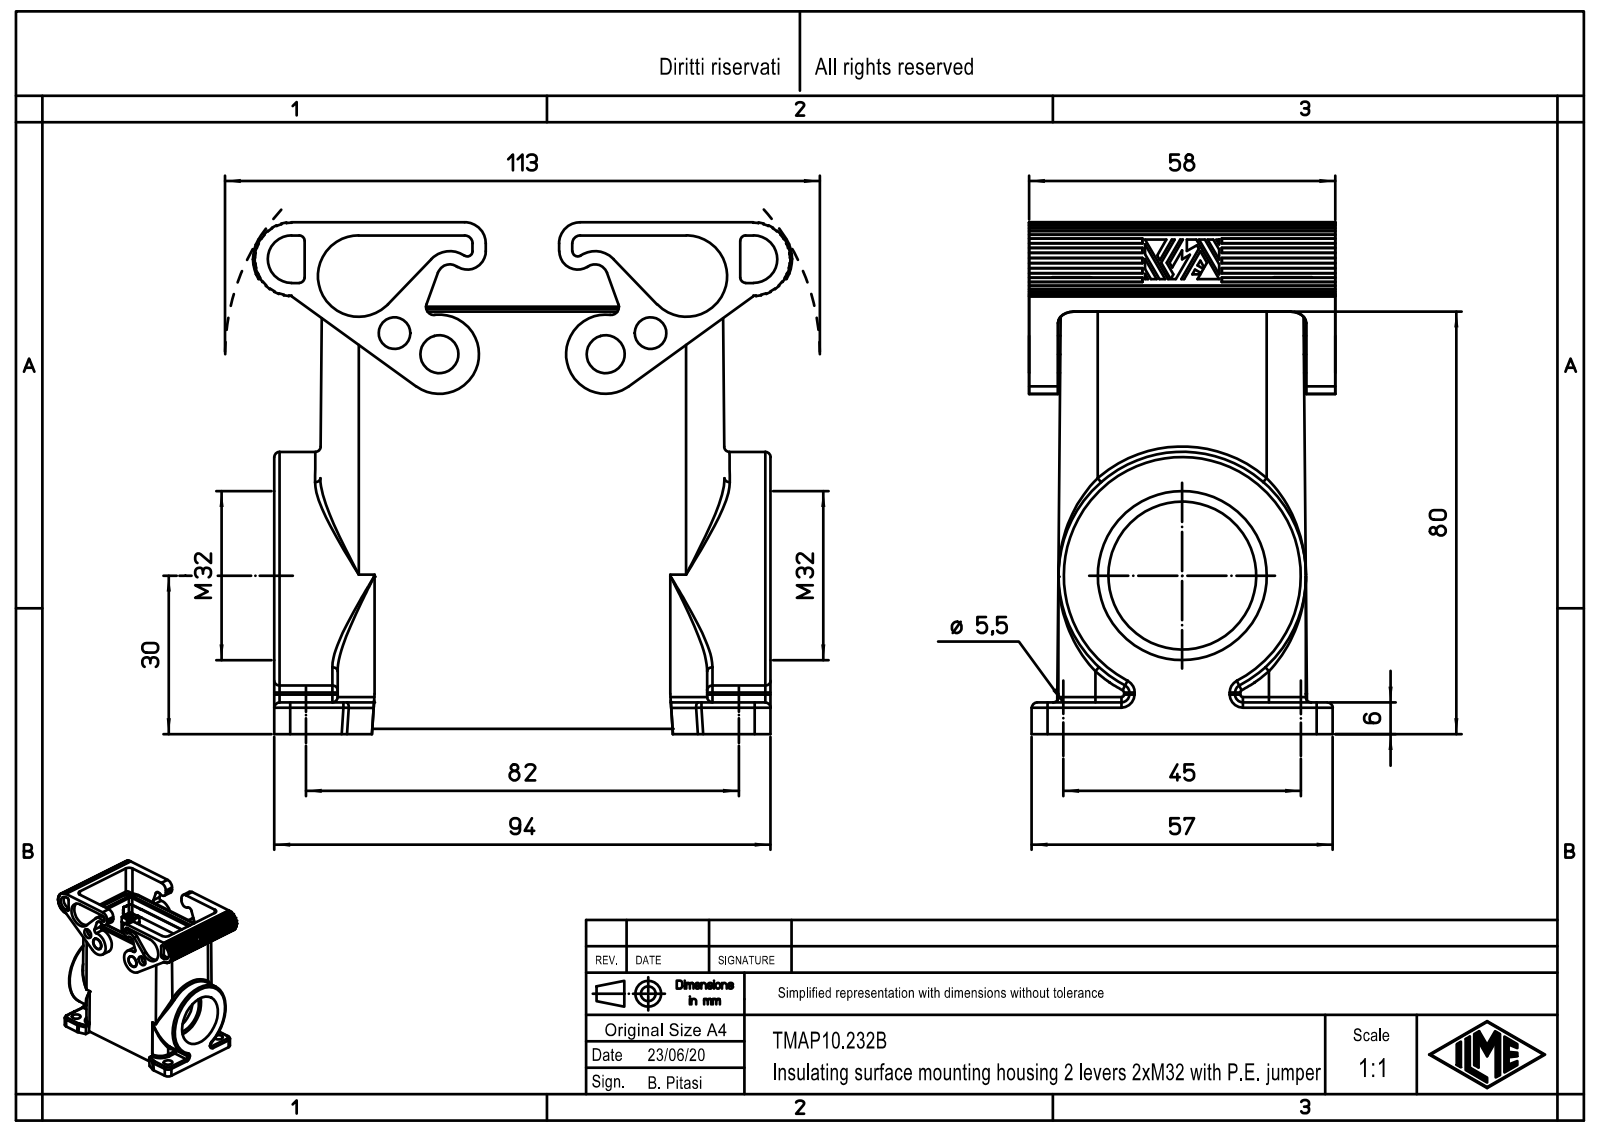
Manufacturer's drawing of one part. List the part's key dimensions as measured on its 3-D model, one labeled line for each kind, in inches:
Part name (STEP PRODUCT): TMAP10.232B
STEP written by: Creo Elements/Direct Modeling 20.1B 02-Apr-2019 (C) Parametric Technology GmbH (AUTOMOTIVE_DESIGN)
Units: inches
Bodies: 1 solid, 944 faces (536 planar, 276 cylindrical, 132 other)
Overall size (bounding box): 4.02 × 3.815 × 2.283
Volume: 10.7 in³ · Surface area: 101.5 in²
Round holes (diameter × count): ⌀0.118 ×4, ⌀0.138 ×4, ⌀0.217 ×4, ⌀0.236 ×2, ⌀0.394 ×2, ⌀1.102 ×1, ⌀1.26 ×1
Round bosses / shafts (diameter × count): ⌀0.189 ×4, ⌀0.276 ×2, ⌀1.845 ×1
Partial cylindrical surfaces — rounded edges, fillets, slot ends (radius × count): R0.039 ×20, R0.059 ×20, R0.118 ×12, R0.138 ×6, R0.276 ×6, R0.02 ×4, R0.051 ×4, R0.063 ×4
Main face-to-face distances: 1.598, 0.217, 2.067, 0.039, 2.465, 0.098, 2.185, 0.256, 1.969, 0.118
Hole centre spacings: 0.606, 1.5, 2.759, 3.081, 0.37, 1.063, 1.583, 1.772
